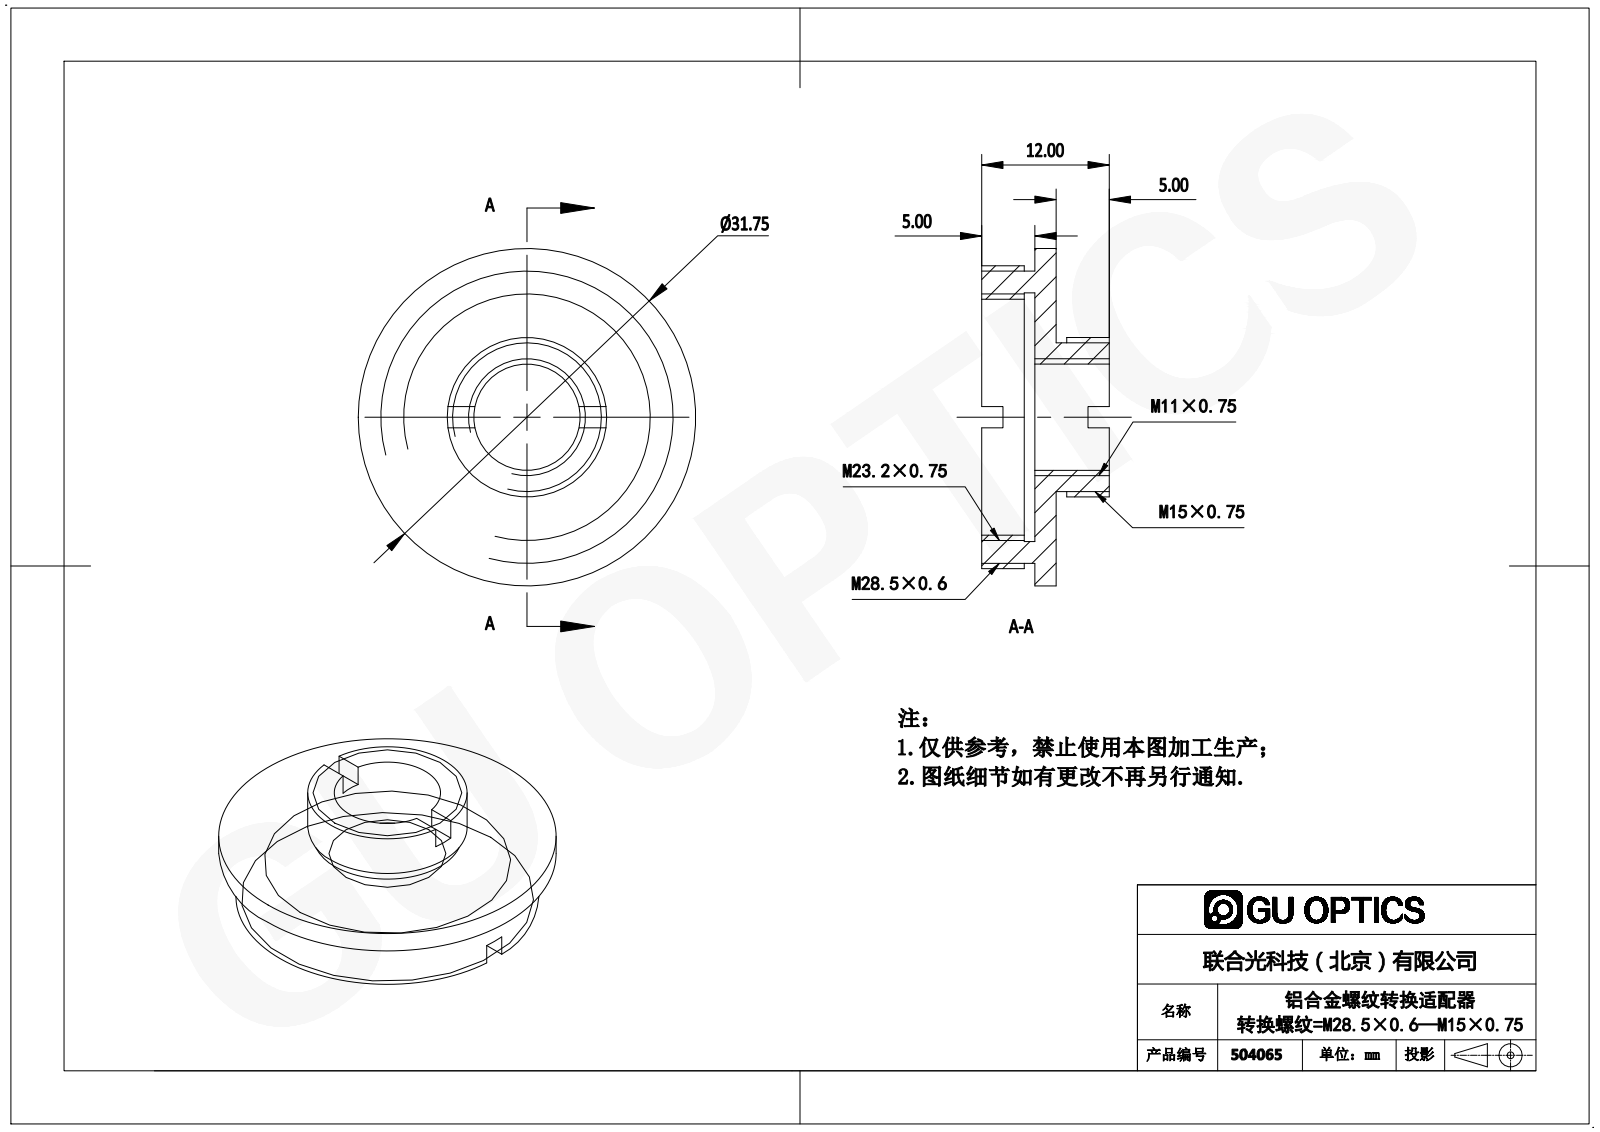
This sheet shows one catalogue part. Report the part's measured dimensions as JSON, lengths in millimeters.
{"part_name": "504065", "step_written_by": "SolidWorks 2016 (AUTOMOTIVE_DESIGN)", "units": "millimeters", "bodies": {"solids": 1, "faces": 38, "planar": 22, "cylindrical": 16, "other": 0}, "overall_size": [31.75, 31.75, 12], "volume_mm3": 3017, "surface_area_mm2": 3108, "round_holes": [[10, 1], [22.2, 1], [23.4, 1]], "round_bosses_or_shafts": [[31.75, 1], [28.5, 1], [27.5, 1], [15, 1], [14, 1]], "face_to_face_distances": [2, 5, 7, 4, 3, 8, 1, 12, 10, 6]}
